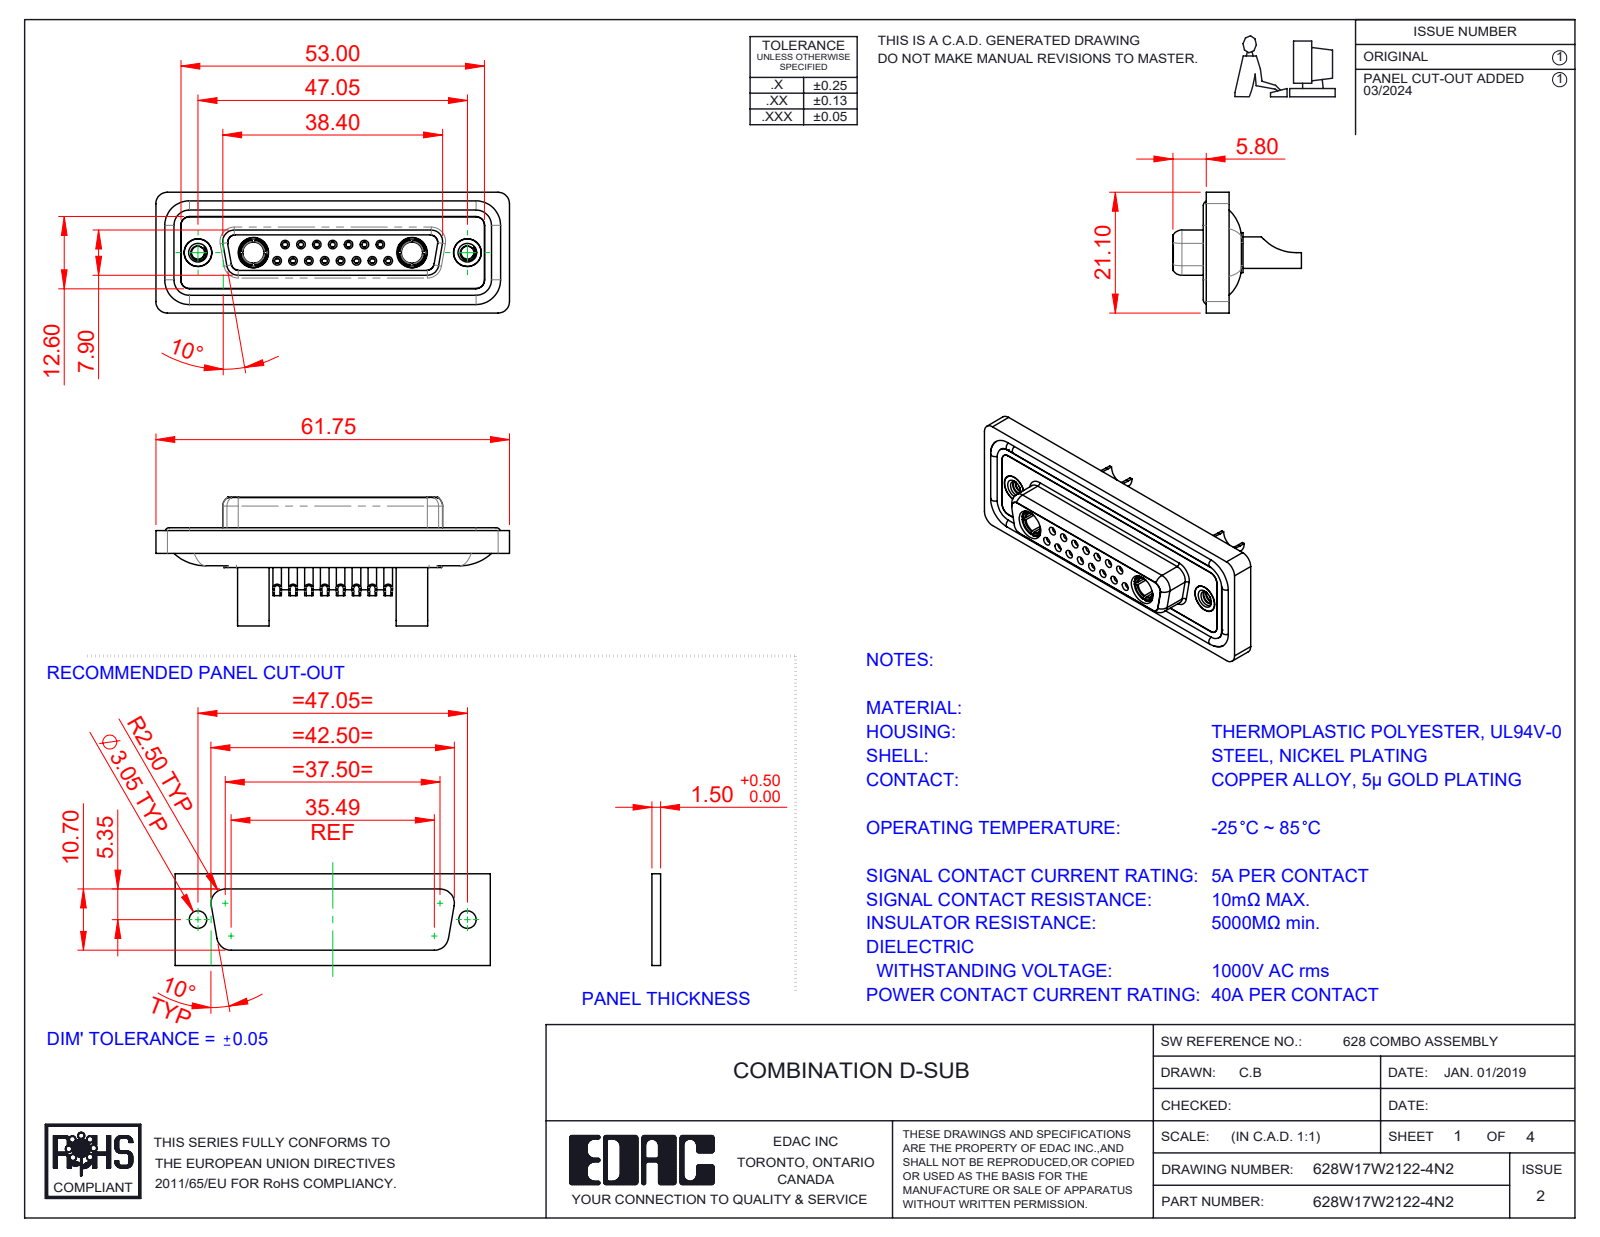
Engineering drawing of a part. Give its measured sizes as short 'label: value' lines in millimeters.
name: Power Socket_40A SC; 628Combo Threaded Rivet_2; 628Combo Shell Rear_25 Contacts; 628Combo Contact Row 1_22 (+5 more)
written by: SolidWorks 2023 (CONFIG_CONTROL_DESIGN)
unit: mm
bodies: 26 solids, 1365 faces (422 planar, 551 cylindrical, 392 other)
size: 61.75 × 22.45 × 21.1
volume: 8 435 mm³; area: 14 295 mm²
holes: 15× ⌀0.9, 15× ⌀1, 15× ⌀1.1, 15× ⌀1.5, 15× ⌀2, 8× ⌀1.6, 7× ⌀1.7, 4× ⌀4.85, 2× ⌀2.26, 2× ⌀3.7, 2× ⌀4, 2× ⌀4.05
bosses: 15× ⌀2.2, 11× ⌀1.6, 2× ⌀5.5, 2× ⌀5.2, 2× ⌀4.96, 2× ⌀4.95, 2× ⌀4.8, 2× ⌀4.75
rounds: 22× R1.5, 18× R2, 8× R1.35, 8× R1.6, 6× R1, 4× R0.25, 4× R0.5, 4× R0.6
face distances: 0.4, 7.45, 1.8, 5.65, 6.6, 0.5, 7.05, 1.6, 2.9, 1.1
hole spacings: 3.16, 2.77, 8.31, 5.54, 5.03, 5.04, 7.49, 11.08
